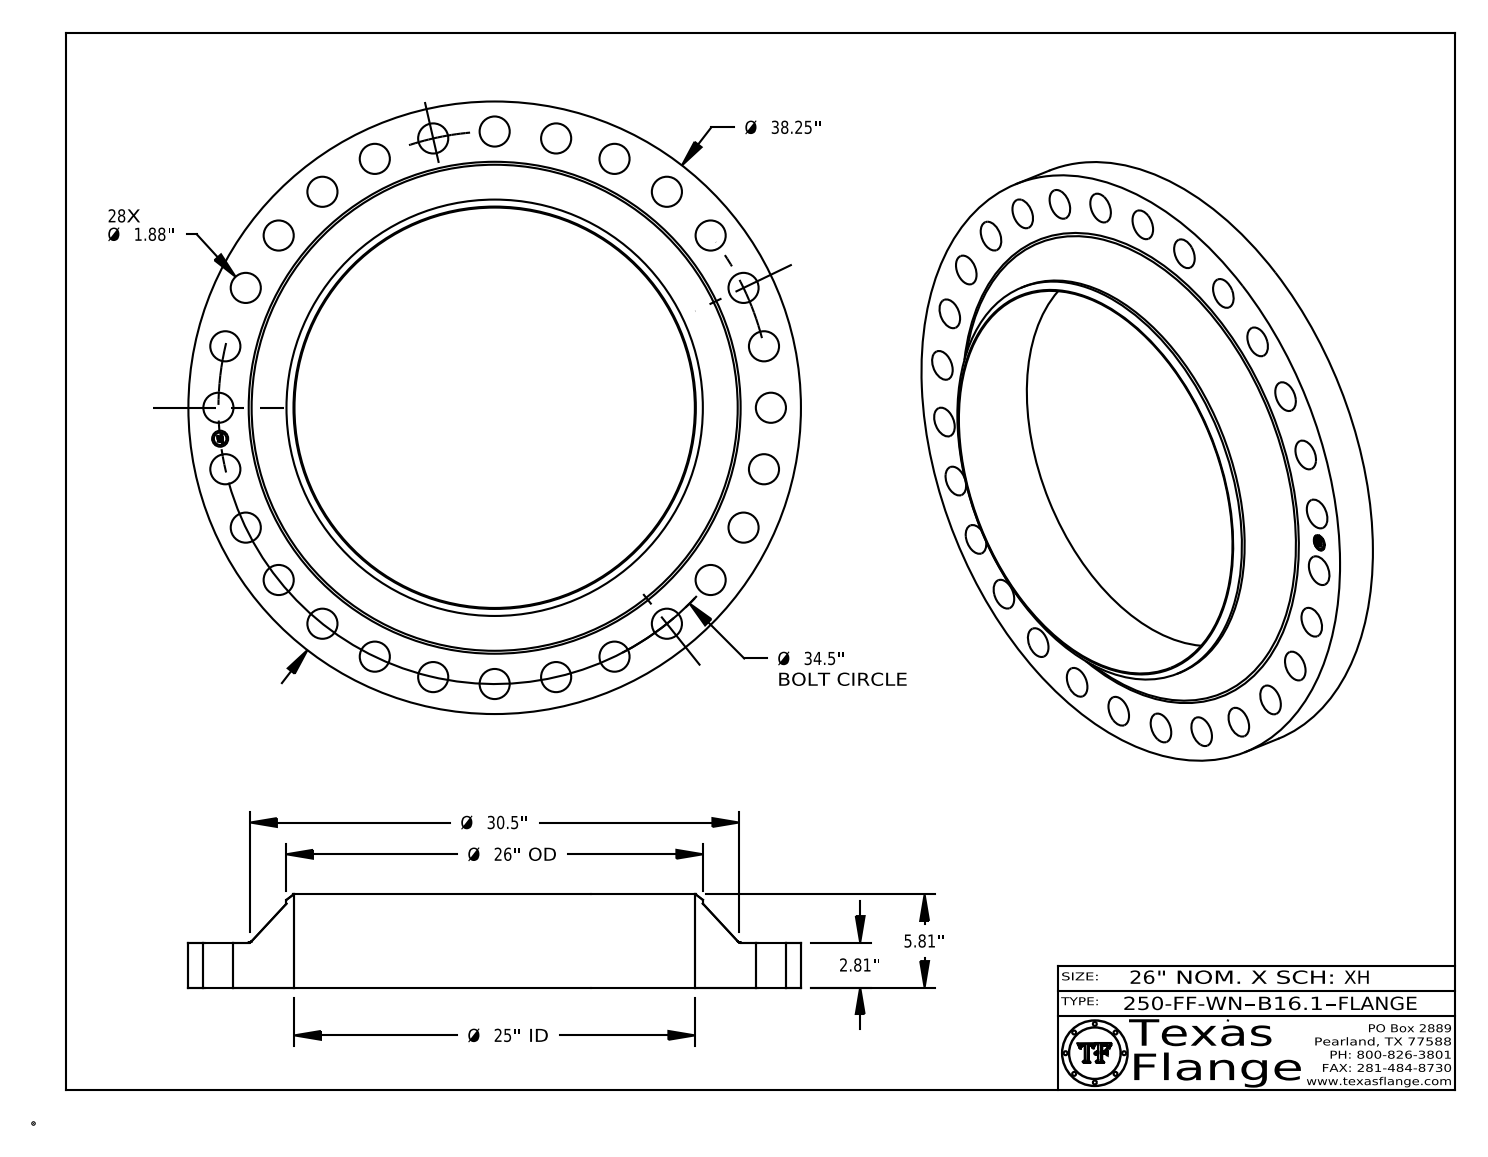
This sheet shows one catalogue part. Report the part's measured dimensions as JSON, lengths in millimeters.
{"part_name": "250-FF-WN, B16.1", "step_written_by": "CATIA V5 STEP AP214 (AUTOMOTIVE_DESIGN)", "units": "millimeters", "bodies": {"solids": 1, "faces": 456, "planar": 368, "cylindrical": 82, "other": 6}, "overall_size": [971.6, 971.6, 147.6], "volume_mm3": 32480000, "surface_area_mm2": 1639000, "round_holes": [[47.8, 28], [25.4, 1], [635, 1]], "round_bosses_or_shafts": [[1.5, 8], [971.6, 1], [660.4, 1], [20, 1]], "face_to_face_distances": [71.4, 147.6, 76.2, 0.4, 71, 76.6, 7.6, 7.4, 1.4, 4.9], "hole_center_spacings": [438.2, 685.1, 870.8, 380.2, 466.2, 827.1, 854.3, 289.4]}
